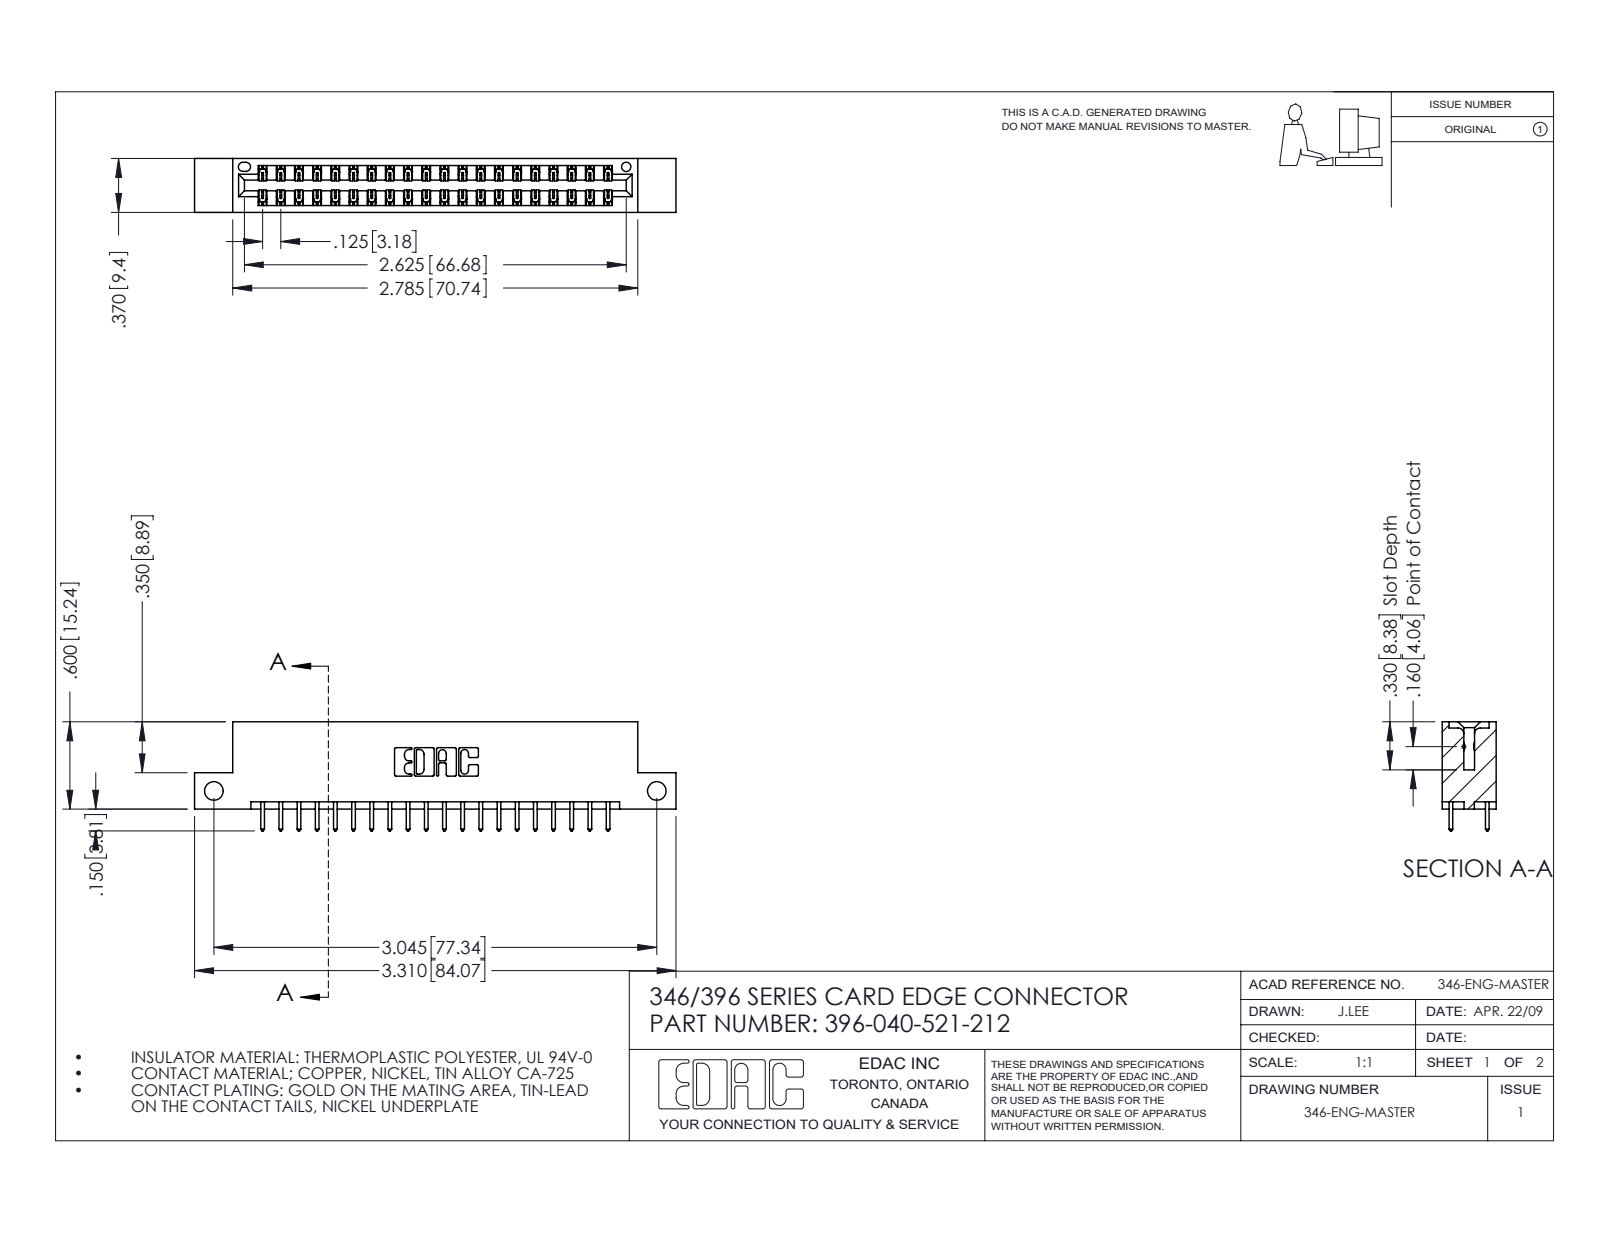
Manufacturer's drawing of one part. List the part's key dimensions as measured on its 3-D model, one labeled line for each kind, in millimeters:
Part name (STEP PRODUCT): 396-040-521-212; 345-292-001_345-293-121; 346 Part_Flush Mounting Lugs - Side Mount
STEP written by: SolidWorks 2016 (CONFIG_CONTROL_DESIGN)
Units: millimetres
Bodies: 41 solids, 2202 faces (1476 planar, 726 cylindrical, 0 other)
Overall size (bounding box): 84.1 × 19.1 × 9.4
Volume: 7 930 mm³ · Surface area: 10 300 mm²
Round holes (diameter × count): ⌀3.3 ×2, ⌀1.6 ×1
Partial cylindrical surfaces — rounded edges, fillets, slot ends (radius × count): R0.2 ×60, R0.3 ×40, R0.3 ×22, R0.2 ×6, R0.8 ×6, R0.7 ×3, R0.4 ×2, R0.6 ×2
Main face-to-face distances: 1.2, 8.2, 6.4, 9.4, 1.8, 7.6, 0.6, 7, 3.8, 5.6
Hole centre spacings: 77.3
